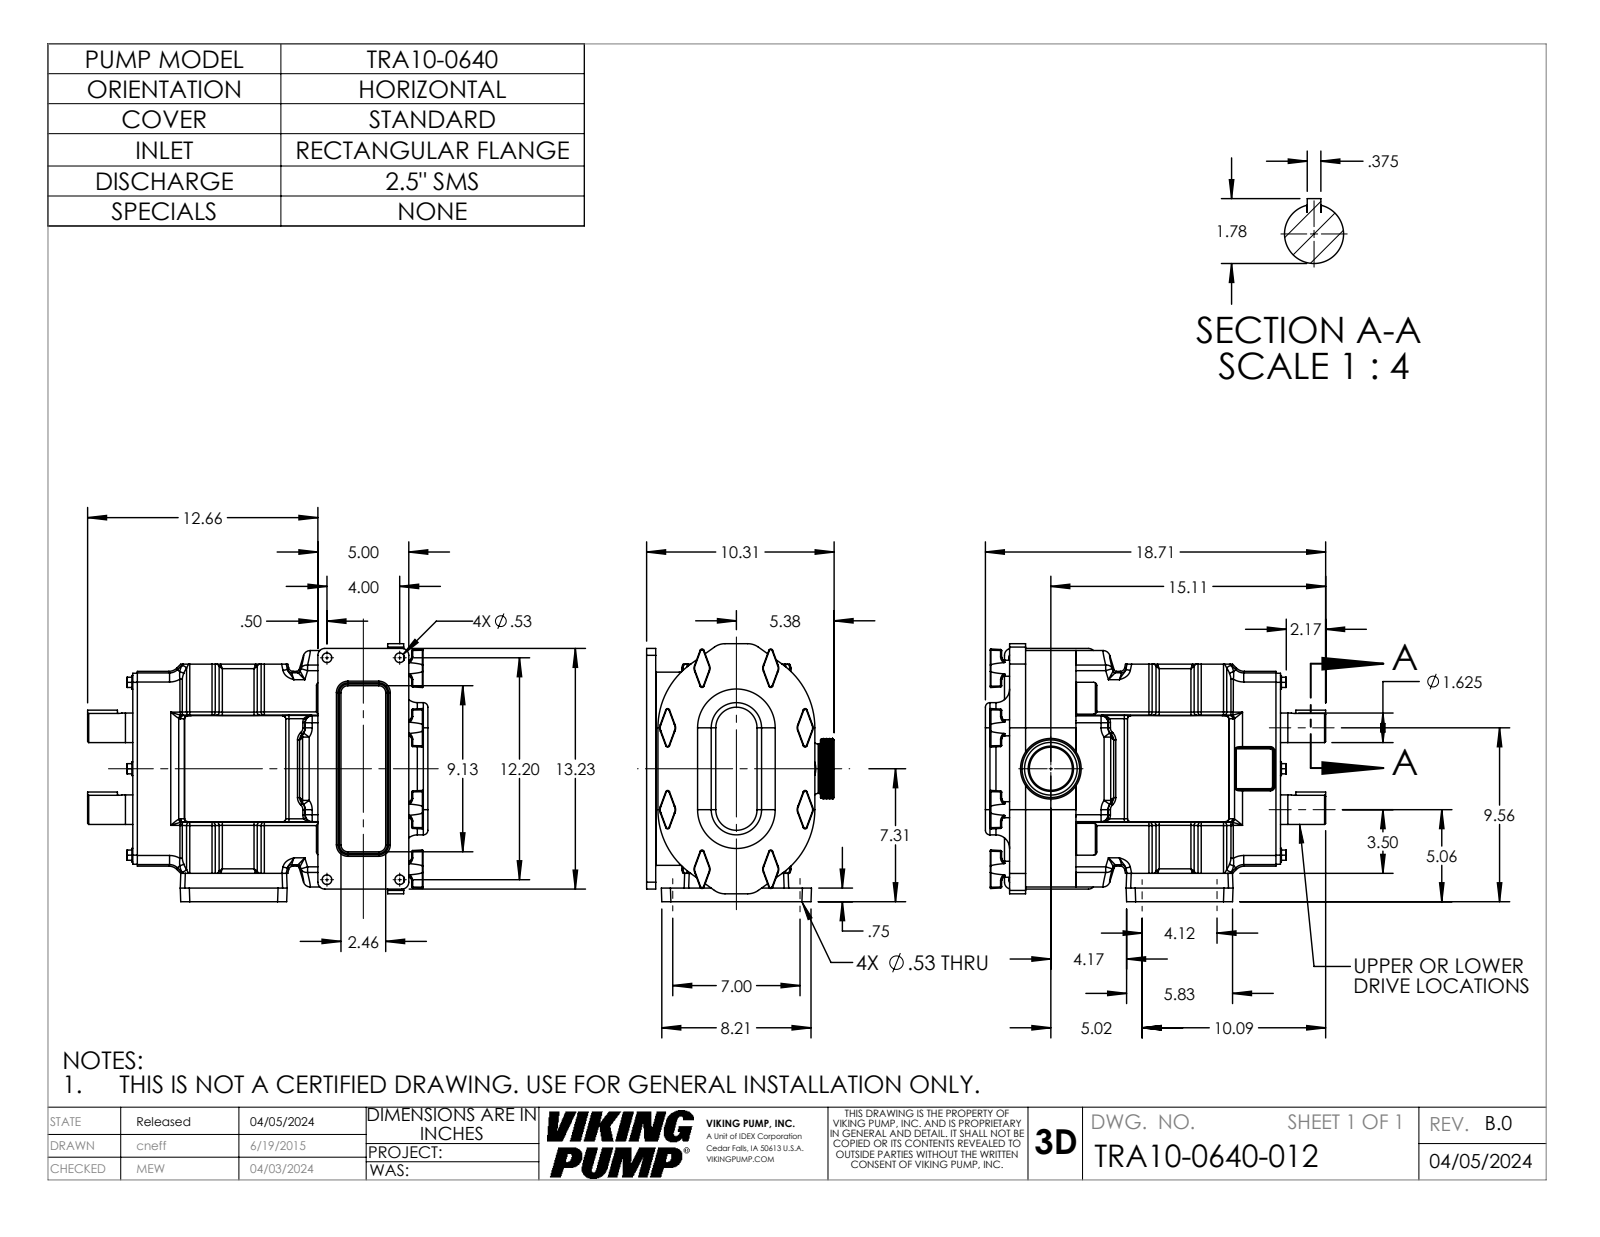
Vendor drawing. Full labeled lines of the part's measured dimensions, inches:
Part name (STEP PRODUCT): 0600SMS25; TRA10-0600-COVER-STD; TRA10-0600-GEARBOX-H; TRA10-0640-012 (+1 more)
STEP written by: SolidWorks 2022 (AUTOMOTIVE_DESIGN)
Units: inches
Bodies: 4 solids, 1116 faces (297 planar, 395 cylindrical, 424 other)
Overall size (bounding box): 18.714 × 14.185 × 10.313
Volume: 1 230 in³ · Surface area: 1 434 in²
Round holes (diameter × count): ⌀0.531 ×8, ⌀2.368 ×1, ⌀2.896 ×1
Round bosses / shafts (diameter × count): ⌀0.88 ×8, ⌀0.75 ×6, ⌀1.624 ×2, ⌀3.335 ×1, ⌀2.704 ×1, ⌀2.49 ×1
Partial cylindrical surfaces — rounded edges, fillets, slot ends (radius × count): R0.18 ×44, R0.06 ×43, R0.03 ×36, R0.38 ×36, R0.25 ×32, R0.12 ×24, R0.5 ×22, R0.09 ×16
Main face-to-face distances: 2.769, 0.5, 1.437, 0.88, 3.649, 7.937, 0.36, 11.25, 14.899, 14.019
Hole centre spacings: 4, 4.12, 6.404, 6.435, 7, 8.122, 12.2, 12.839
